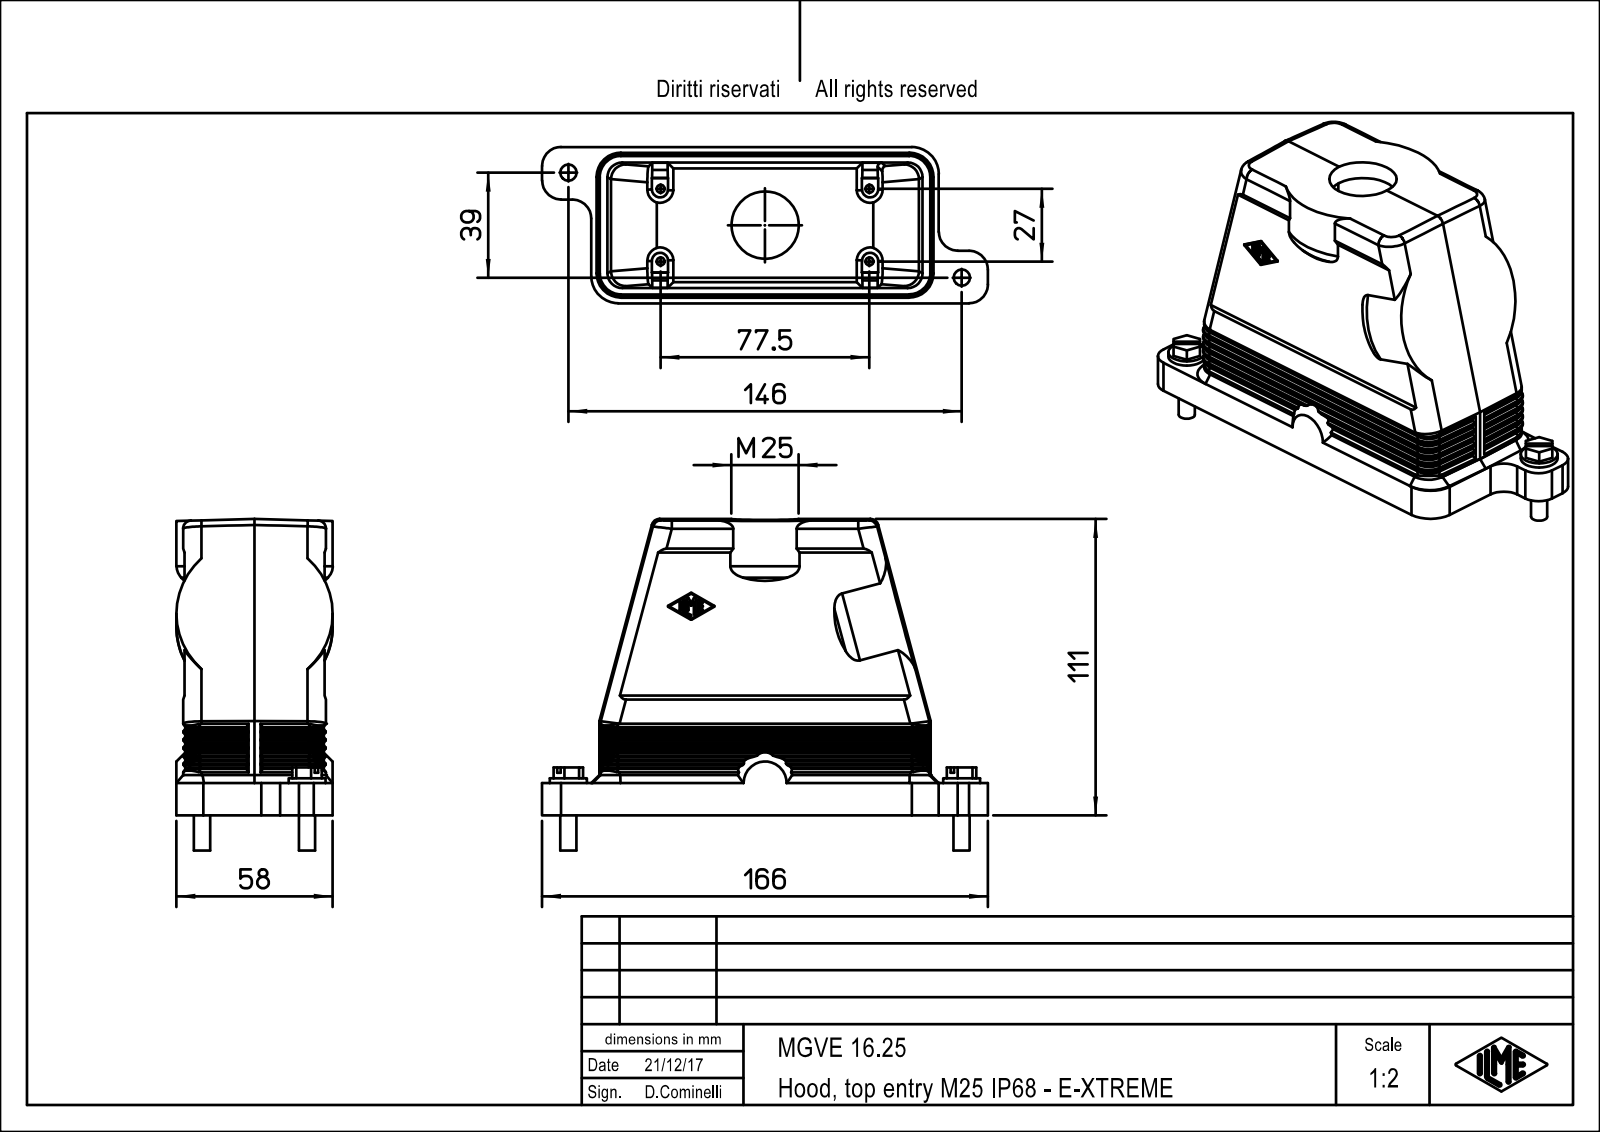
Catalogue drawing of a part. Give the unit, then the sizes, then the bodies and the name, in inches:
Units: inches
Overall size (bounding box): 6.516 × 4.843 × 2.283
Round holes (diameter × count): ⌀0.118 ×4, ⌀0.984 ×1
Round bosses / shafts (diameter × count): ⌀0.539 ×2, ⌀0.236 ×2
Partial cylindrical surfaces — rounded edges, fillets, slot ends (radius × count): R0.276 ×62, R0.013 ×15, R0.217 ×8, R0.335 ×4, R0.007 ×2, R0.394 ×2, R1.142 ×2, R0.007 ×1
Main face-to-face distances: 2.047, 0.118, 2.165, 0.098, 0.02, 2.185, 2.067, 3.071, 0.131, 0.066
Hole centre spacings: 1.615, 1.063, 3.051, 3.231
Volume: 11.48 in³ · Surface area: 132.2 in²
Bodies: 1 solid, 534 faces (254 planar, 124 cylindrical, 156 other)
Part name (STEP PRODUCT): MGVE_16.25
STEP written by: PTC Creo Elements/Direct Modeling 19.0E 27-Jun-2016 (C) Parametric Technology GmbH (AUTOMOTIVE_DESIGN)
